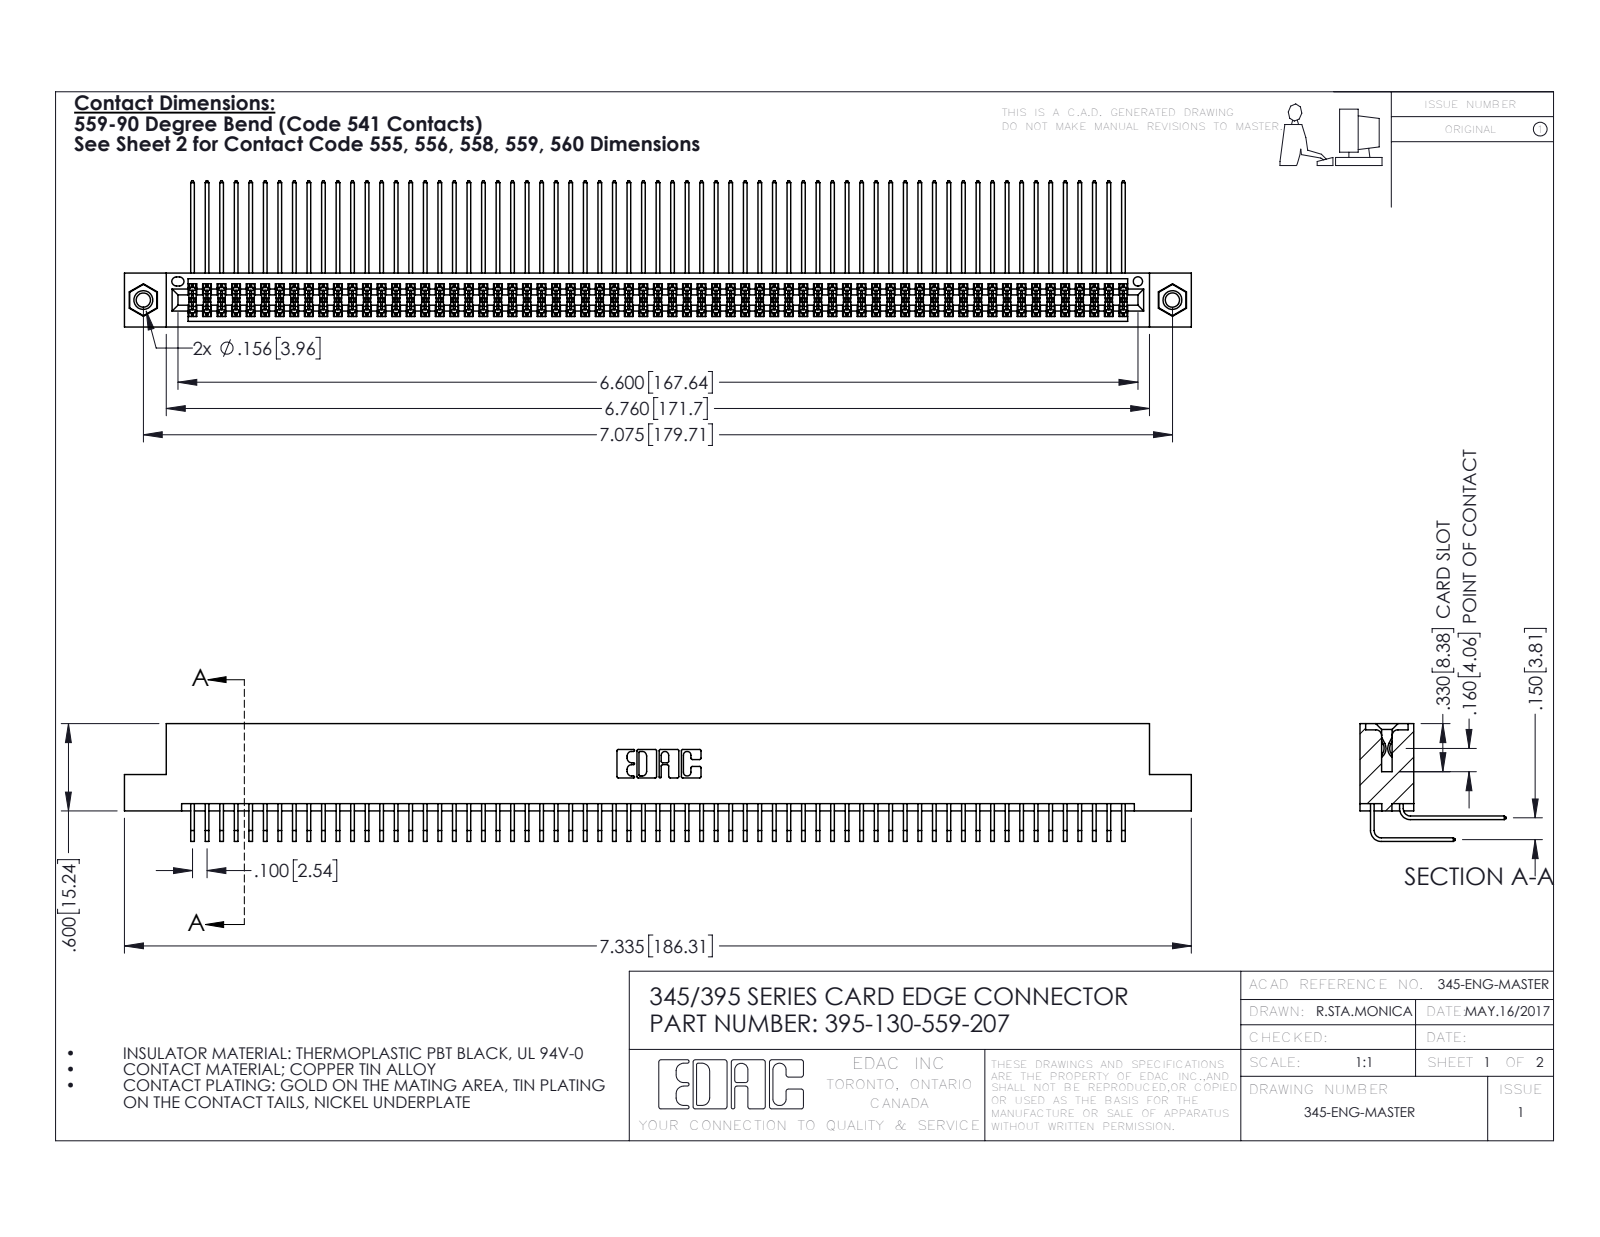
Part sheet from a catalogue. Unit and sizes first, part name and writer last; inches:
Units: inches
Overall size (bounding box): 7.335 × 1.005 × 0.809
Round holes (diameter × count): ⌀0.098 ×2, ⌀0.125 ×2, ⌀0.156 ×2, ⌀0.064 ×1
Round bosses / shafts (diameter × count): ⌀0.155 ×2
Partial cylindrical surfaces — rounded edges, fillets, slot ends (radius × count): R0.006 ×196, R0.01 ×22, R0.007 ×6, R0.031 ×6, R0.026 ×3, R0.014 ×2, R0.019 ×2, R0.022 ×2
Main face-to-face distances: 0.072, 0.298, 0.2, 0.37, 0.098, 0.272, 0.025, 0.225, 0.175, 0.15
Hole centre spacings: 0.27, 6.839, 7.075
Volume: 1.162 in³ · Surface area: 49.84 in²
Bodies: 133 solids, 6946 faces (4662 planar, 2268 cylindrical, 16 other)
Part name (STEP PRODUCT): 345-250-001_345-250-005-103; 345-292-001_559 Tail - 2; 345-292-001_558 559 Tail - 1; 395-130-559-207 (+1 more)
STEP written by: SolidWorks 2016 (CONFIG_CONTROL_DESIGN)
